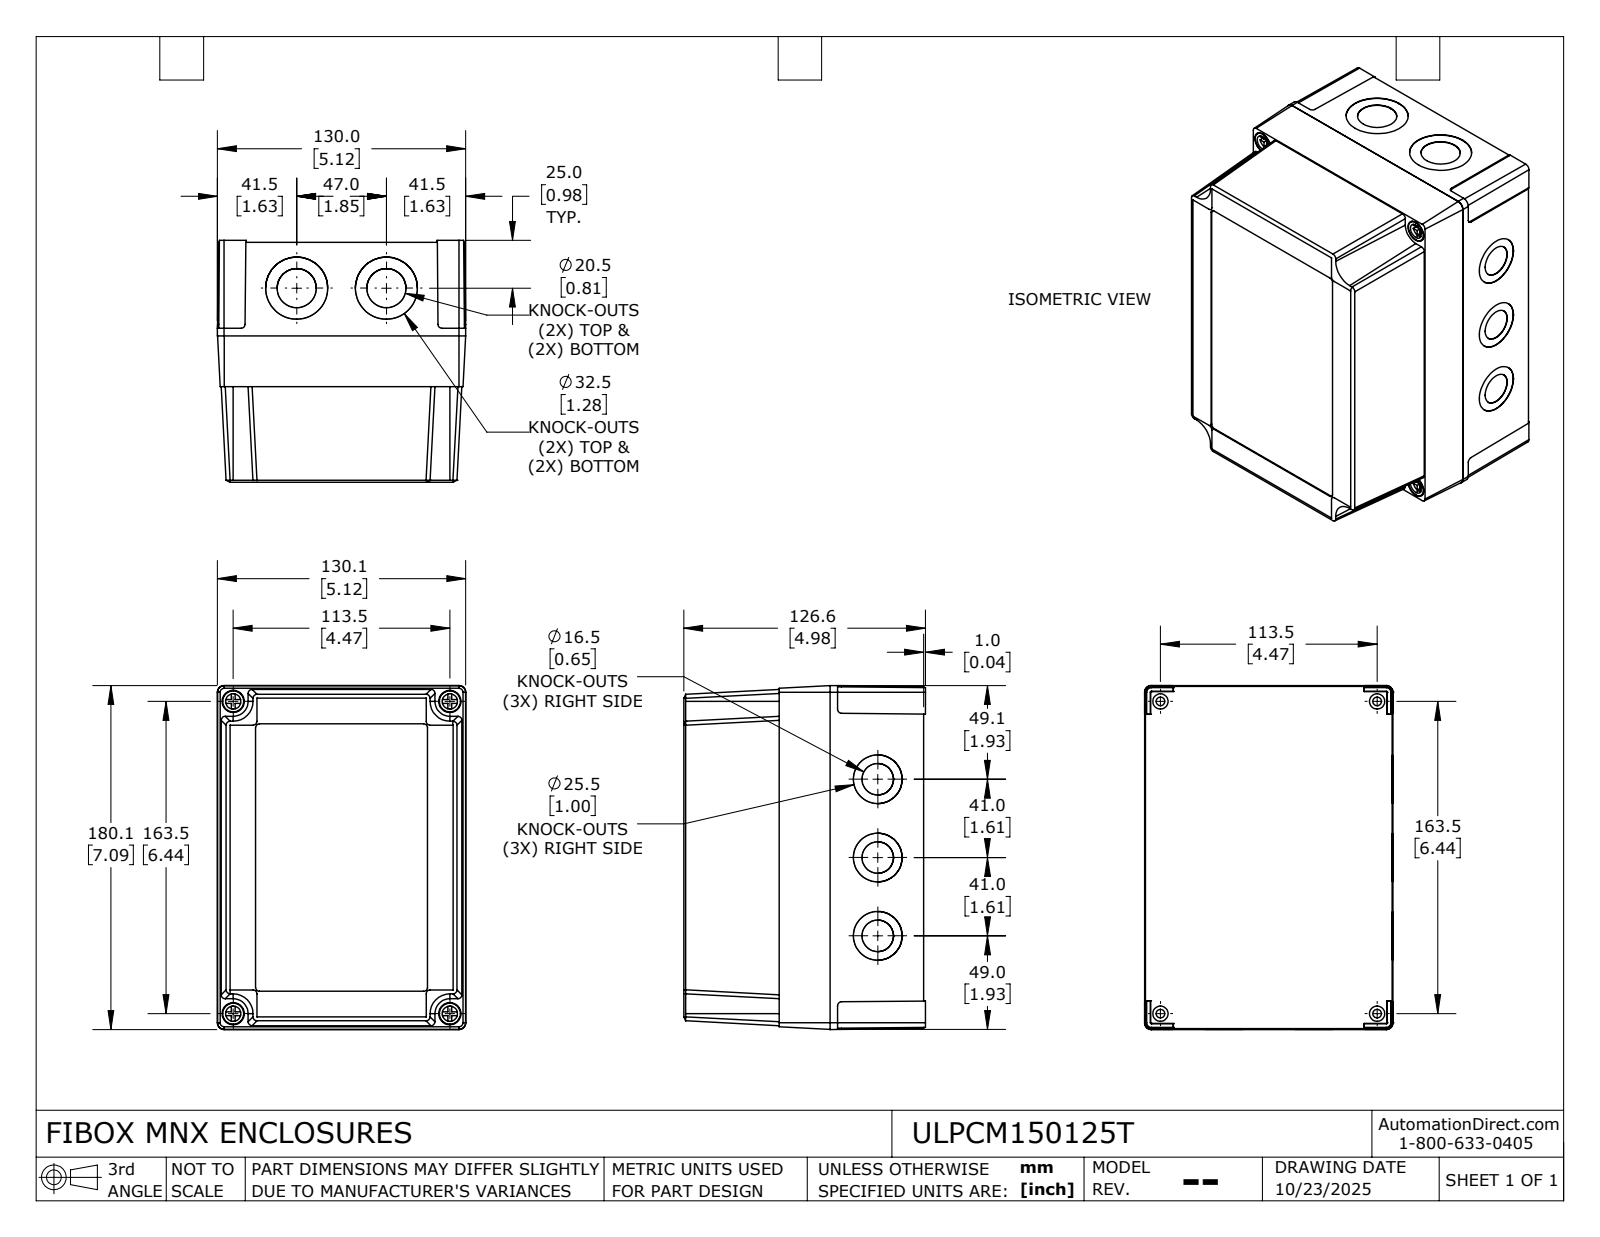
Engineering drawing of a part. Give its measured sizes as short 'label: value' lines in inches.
name: ULPCM150125T_Default
written by: SolidWorks 2024 (CONFIG_CONTROL_DESIGN)
unit: in
bodies: 6 solids, 581 faces (335 planar, 200 cylindrical, 46 other)
size: 7.091 × 5.122 × 4.984
volume: 21.92 in³; area: 385.6 in²
holes: 8× ⌀0.126, 8× ⌀0.157, 6× ⌀0.65, 6× ⌀1.004, 4× ⌀0.177, 4× ⌀0.315, 4× ⌀0.457, 4× ⌀0.807, 4× ⌀1.28
bosses: 8× ⌀0.315, 8× ⌀0.098, 4× ⌀0.433, 4× ⌀0.283
rounds: 8× R0.079, 8× R0.083, 6× R0.056, 4× R0.021, 4× R0.197, 2× R0.023
face distances: 0.055, 0.118, 4.831, 4.713, 0.165, 4.925, 4.807, 0.094, 0.078, 0.022
hole spacings: 1.333, 1.614, 1.939, 1.969, 2.281, 3.252, 3.276, 4.054
